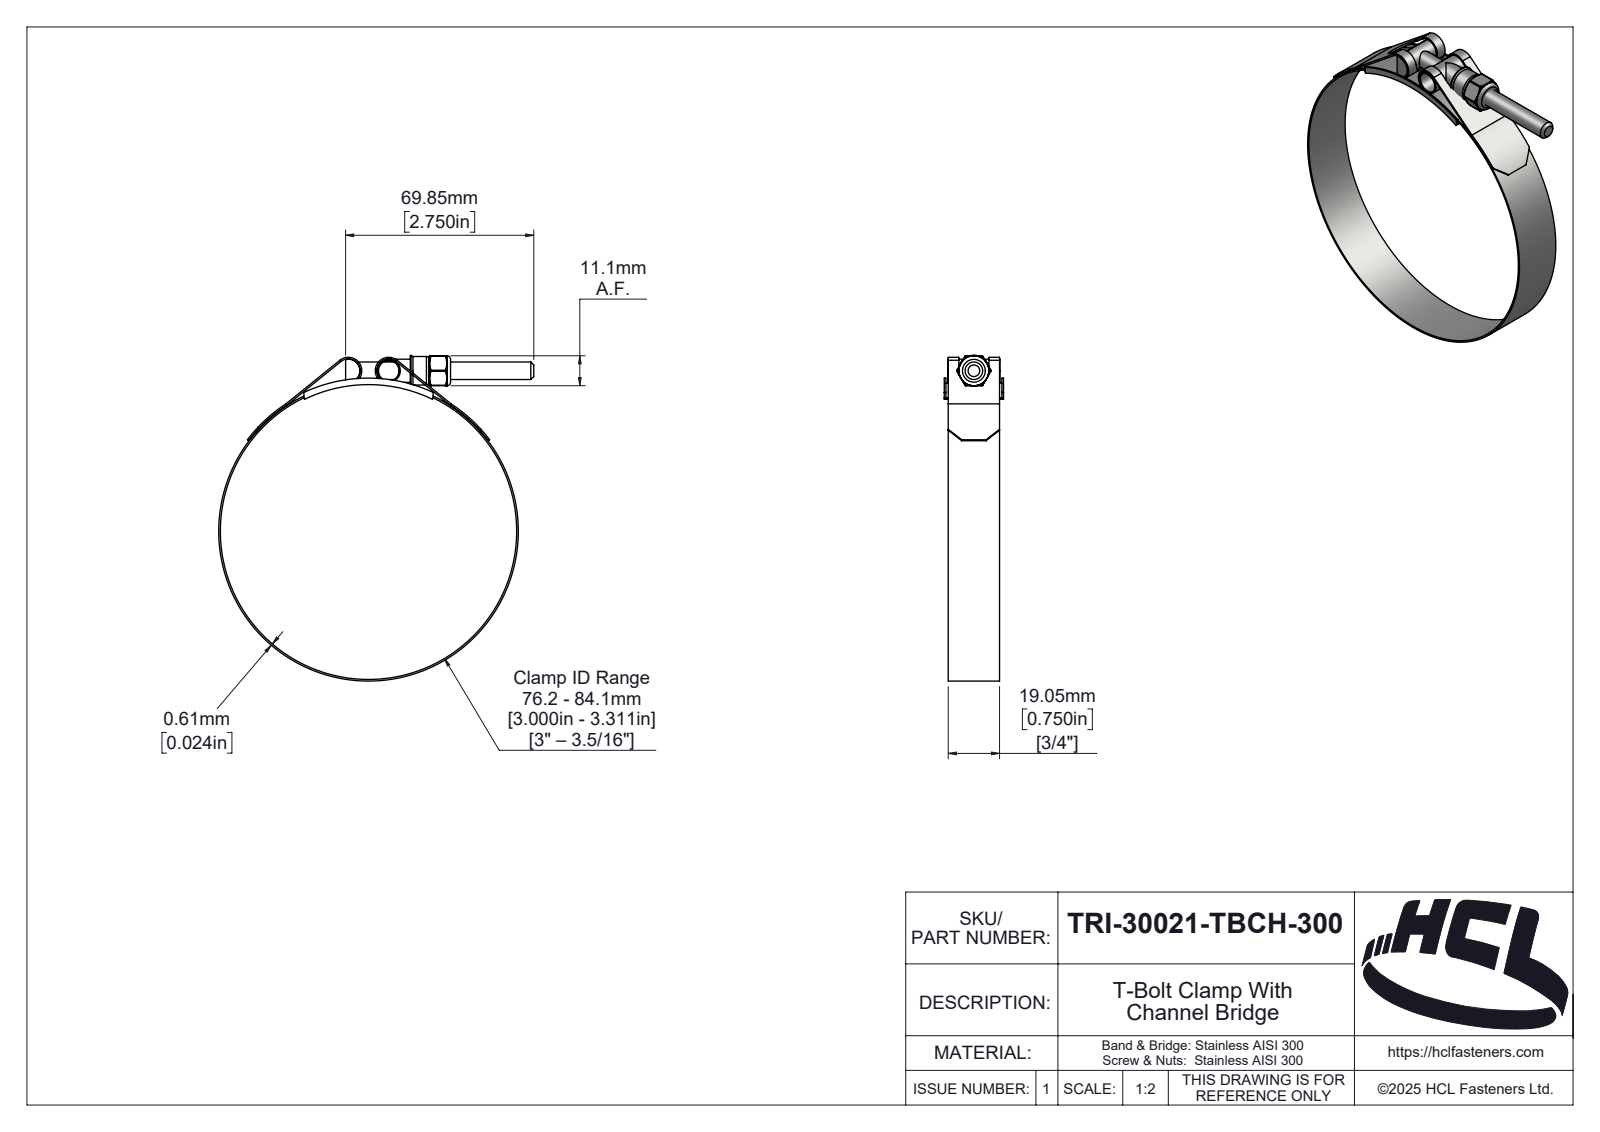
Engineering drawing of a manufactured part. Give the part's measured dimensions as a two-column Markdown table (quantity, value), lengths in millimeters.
| quantity | value |
| --- | --- |
| part name | TRI-30021-TBCH-300 |
| STEP written by | SolidWorks 2025 (AUTOMOTIVE_DESIGN) |
| units | millimeters |
| bodies | 6 solids, 330 faces (46 planar, 122 cylindrical, 162 other) |
| overall size | 120.86 × 116.96 × 22 |
| volume | 9 900 mm³ |
| surface area | 23 824 mm² |
| round holes (diameter × count) | 5.4 × 1, 6.35 × 1, 6.5 × 1, 7.58 × 1, 110 × 1 |
| round bosses / shafts (diameter × count) | 8.58 × 2, 111.22 × 1, 10.58 × 1 |
| partial cylindrical surfaces (radius × count) | 0.39 × 6, 0.5 × 2, 4.39 × 2, 5 × 2, 0.59 × 1, 2.42 × 1, 3.03 × 1, 3.19 × 1 |
| main face-to-face distances | 0.61, 19.06, 1.47, 20.53, 21.39, 0.86, 19.92, 0.74, 22, 1.35 |
| hole center spacings | 60 |
